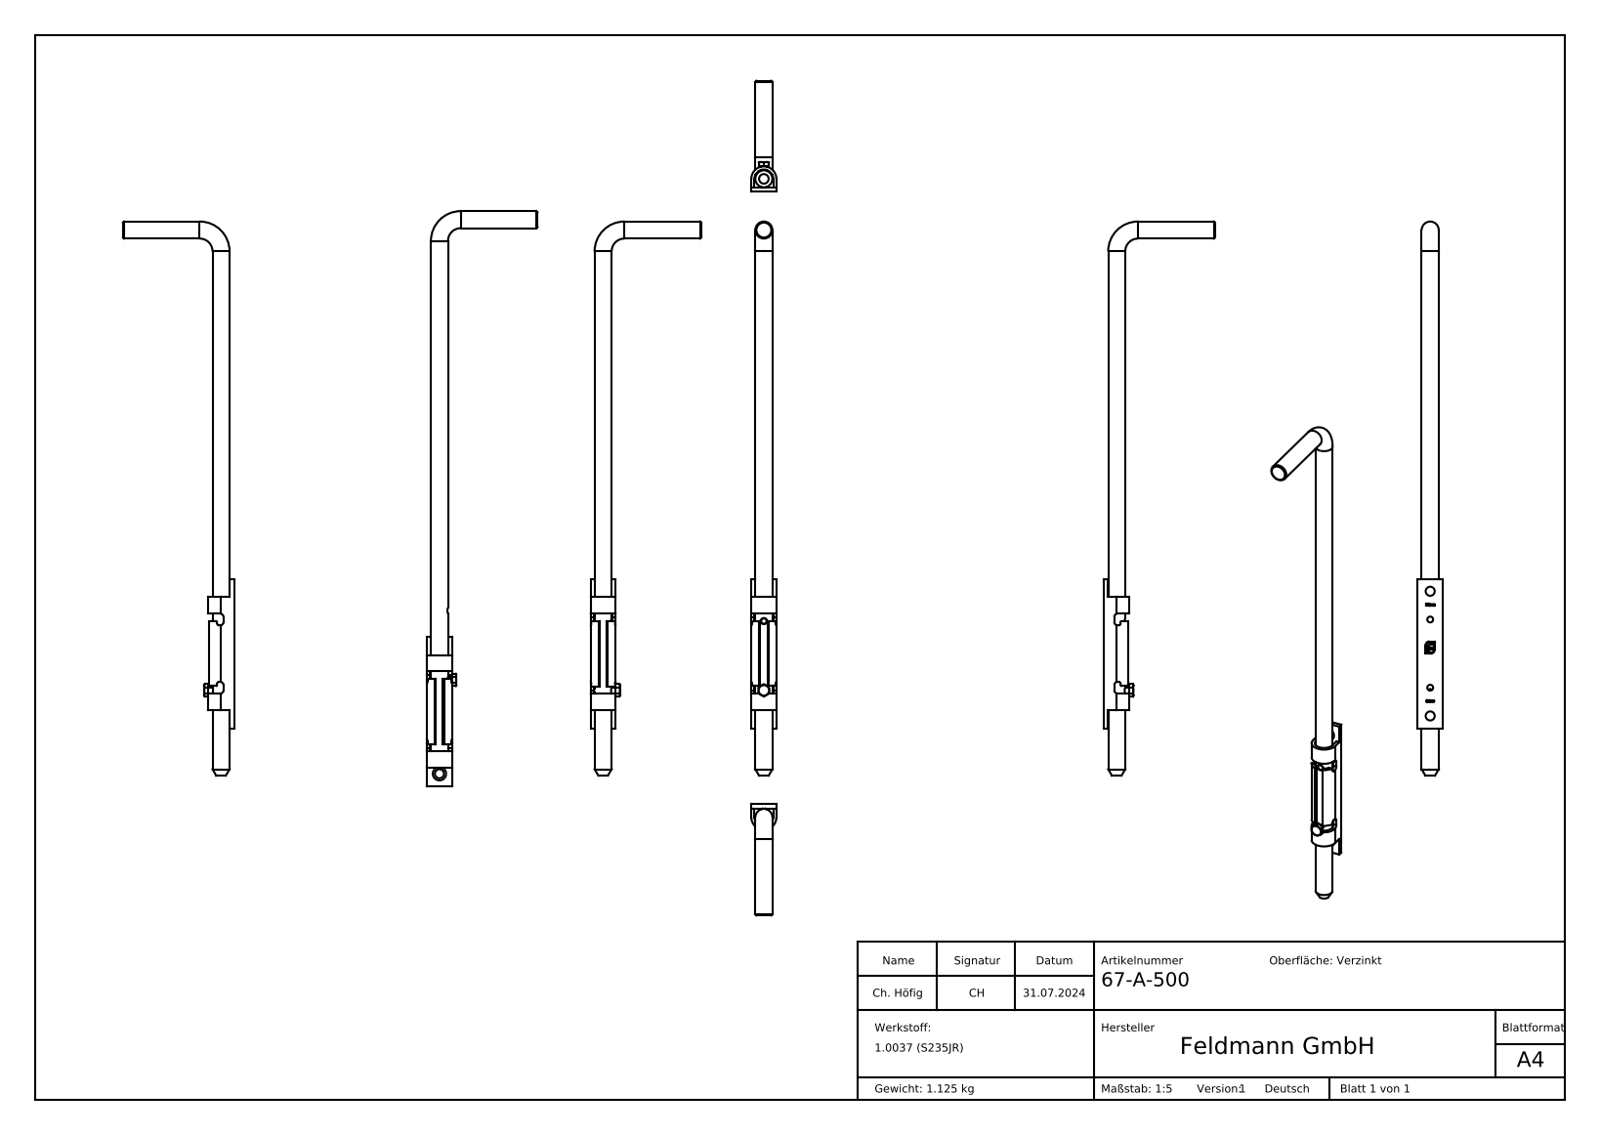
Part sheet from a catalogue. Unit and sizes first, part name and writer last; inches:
Units: inches
Overall size (bounding box): 20.472 × 4.104 × 0.925
Round holes (diameter × count): ⌀0.197 ×2, ⌀0.217 ×2, ⌀0.335 ×2
Round bosses / shafts (diameter × count): ⌀0.63 ×2, ⌀0.236 ×1
Partial cylindrical surfaces — rounded edges, fillets, slot ends (radius × count): R0.118 ×4, R0.039 ×2, R0.079 ×2, R0.344 ×1, R0.463 ×1
Main face-to-face distances: 0.157, 0.118, 0.807, 0.925, 0.689, 0.669, 4.843, 1.28, 4.232, 0.61
Hole centre spacings: 1.043, 3.563, 0.059, 0.098, 0.945, 1.102, 2.461, 2.52
Volume: 8.802 in³ · Surface area: 73.98 in²
Bodies: 3 solids, 329 faces (175 planar, 33 cylindrical, 121 other)
Part name (STEP PRODUCT): 67-A-X00 Teil1_67-A-500 Teil1; 67-A-500; DIN 931_DIN 931 M6x20; 67-A-X00 Teil2_67-A-500 Teil2
STEP written by: SolidWorks 2018 (CONFIG_CONTROL_DESIGN)
